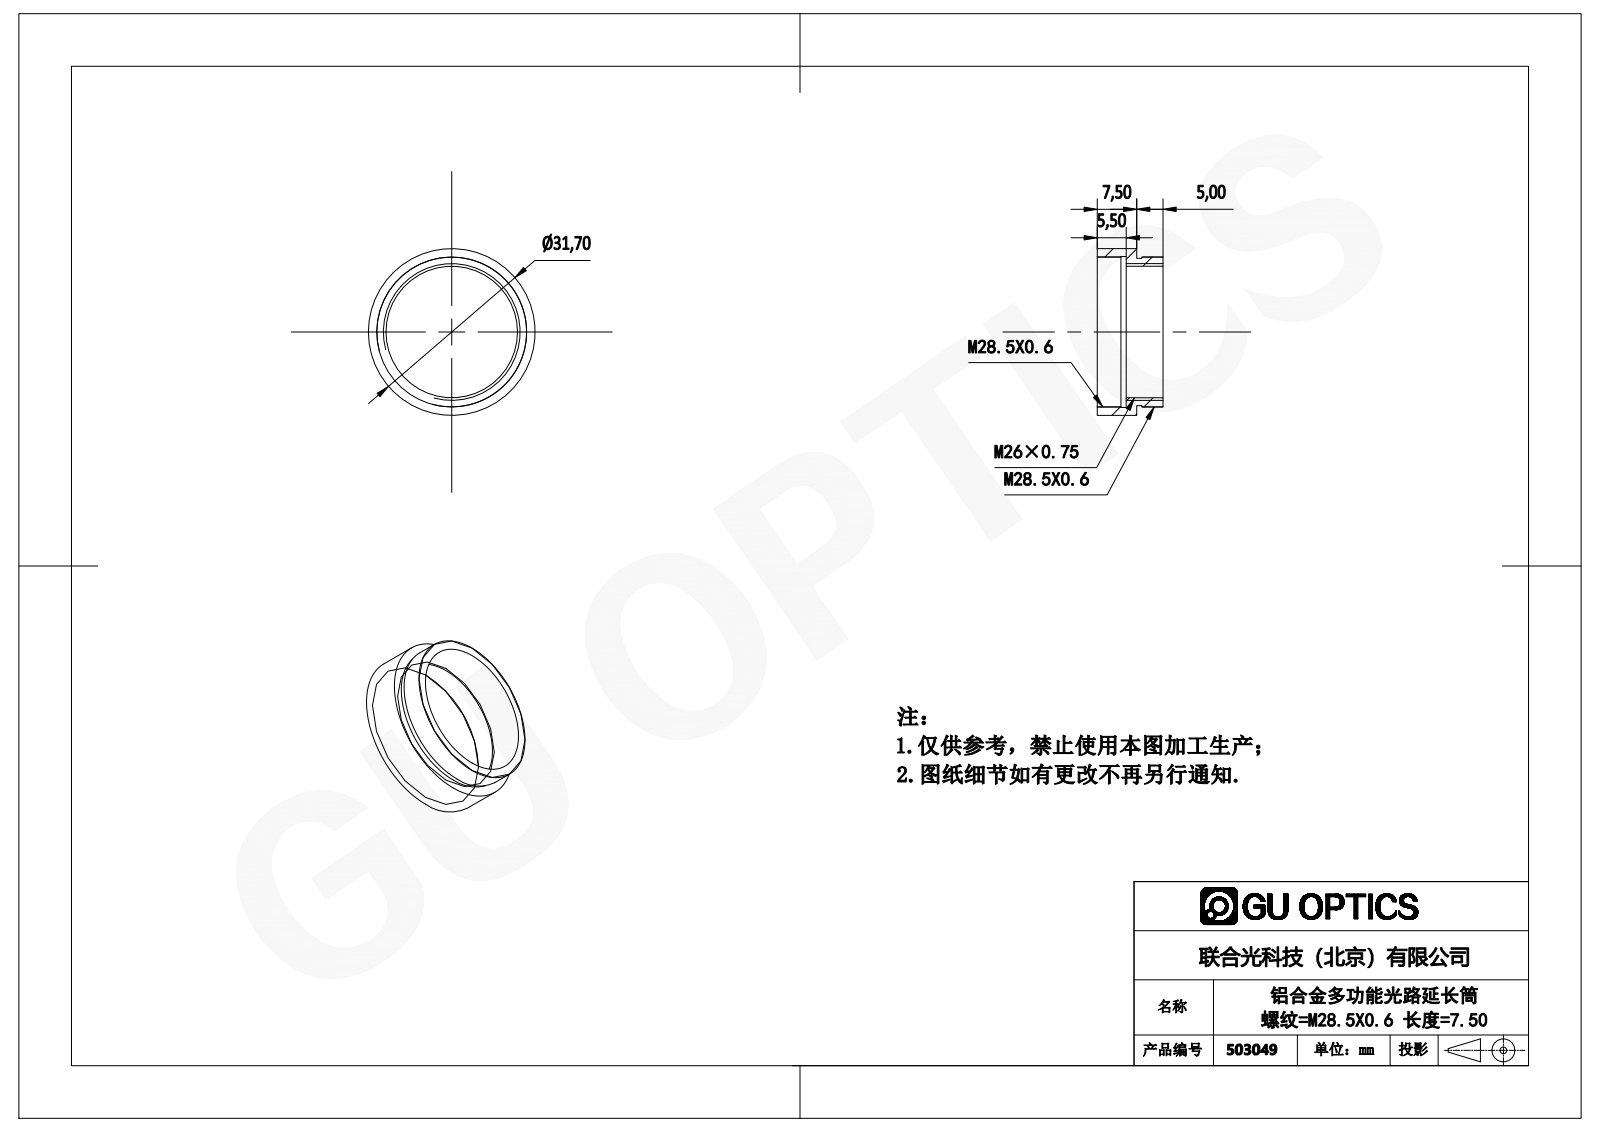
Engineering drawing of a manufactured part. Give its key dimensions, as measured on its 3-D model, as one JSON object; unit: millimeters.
{"part_name": "503049", "step_written_by": "SolidWorks 2016 (AUTOMOTIVE_DESIGN)", "units": "millimeters", "bodies": {"solids": 1, "faces": 18, "planar": 6, "cylindrical": 12, "other": 0}, "overall_size": [31.7, 31.7, 12.5], "volume_mm3": 2133, "surface_area_mm2": 2895, "round_holes": [[25, 1], [28.5, 1], [28.7, 1]], "round_bosses_or_shafts": [[31.7, 1], [28, 1]], "face_to_face_distances": [2, 5.5, 7.5, 12.5, 7, 5, 1, 3, 4, 8.5]}
